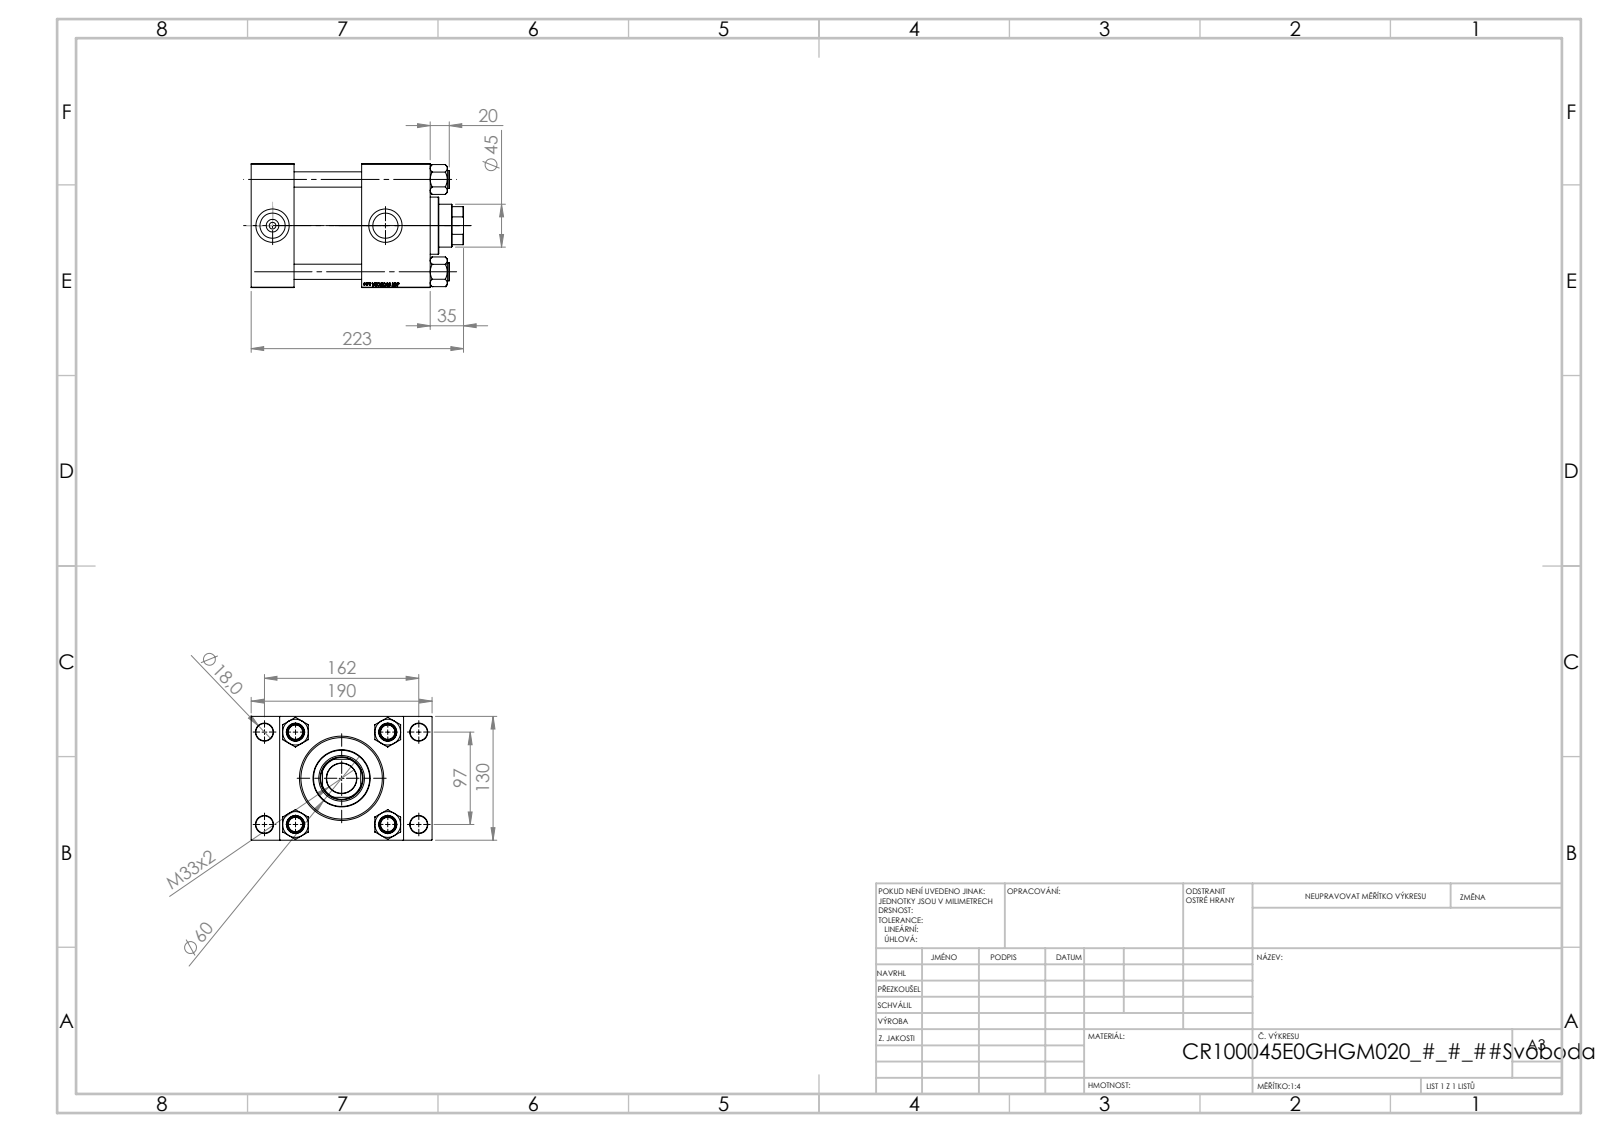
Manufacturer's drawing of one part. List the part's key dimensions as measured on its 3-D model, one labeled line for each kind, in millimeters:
Part name (STEP PRODUCT): V215CR_E_Body; NUT_M5_E; V215CR_TYCINKA_E; V215_VC_A (+1 more)
STEP written by: SolidWorks 2019 (CONFIG_CONTROL_DESIGN)
Units: millimetres
Bodies: 11 solids, 1184 faces (546 planar, 86 cylindrical, 552 other)
Overall size (bounding box): 223 × 190 × 130
Volume: 2 744 000 mm³ · Surface area: 369 920 mm²
Round holes (diameter × count): ⌀16 ×4, ⌀18 ×4, ⌀7 ×2, ⌀26.44 ×2, ⌀35 ×2, ⌀31.5 ×1, ⌀45 ×1, ⌀48 ×1, ⌀76 ×1, ⌀85.5 ×1, ⌀100 ×1
Round bosses / shafts (diameter × count): ⌀19 ×4, ⌀106 ×1, ⌀60 ×1
Partial cylindrical surfaces — rounded edges, fillets, slot ends (radius × count): R22 ×1
Main face-to-face distances: 130, 45, 188, 143, 30, 160, 116, 71, 72, 20
Hole centre spacings: 32.55, 68.52, 94.41, 96.9, 102.27, 129.45, 161.73, 97
